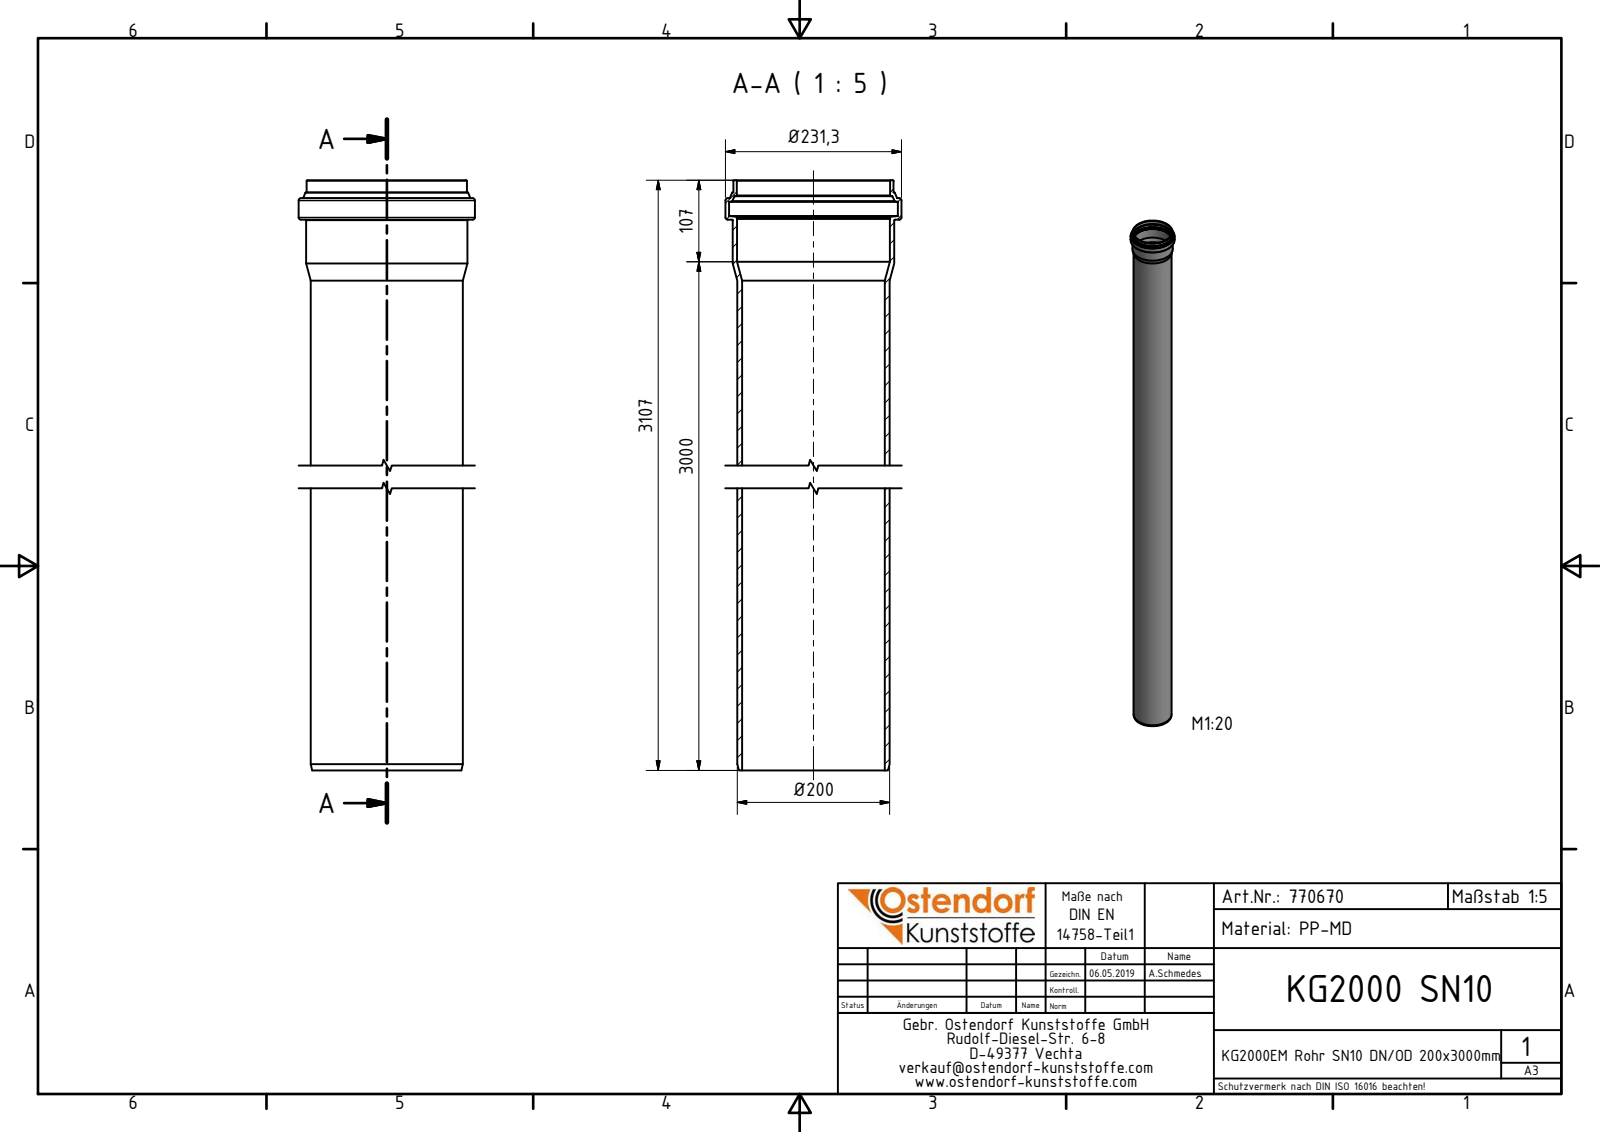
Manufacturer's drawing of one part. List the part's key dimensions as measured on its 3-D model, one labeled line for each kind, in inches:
Part name (STEP PRODUCT): 770670 KG2000EM Rohr SN10 DN-OD200x3000
STEP written by: Autodesk Inventor 2016 (AUTOMOTIVE_DESIGN)
Units: inches
Bodies: 1 solid, 37 faces (6 planar, 9 cylindrical, 22 other)
Overall size (bounding box): 122.323 × 9.106 × 9.106
Volume: 716.4 in³ · Surface area: 5 926 in²
Round holes (diameter × count): ⌀7.386 ×1, ⌀7.906 ×1, ⌀7.913 ×1, ⌀8.736 ×1
Round bosses / shafts (diameter × count): ⌀9.106 ×1, ⌀8.346 ×1, ⌀8.283 ×1, ⌀7.874 ×1
Main face-to-face distances: 120.287, 121.398, 1.11, 122.323, 2.035, 0.925, 121.692, 1.404, 0.294, 0.631
